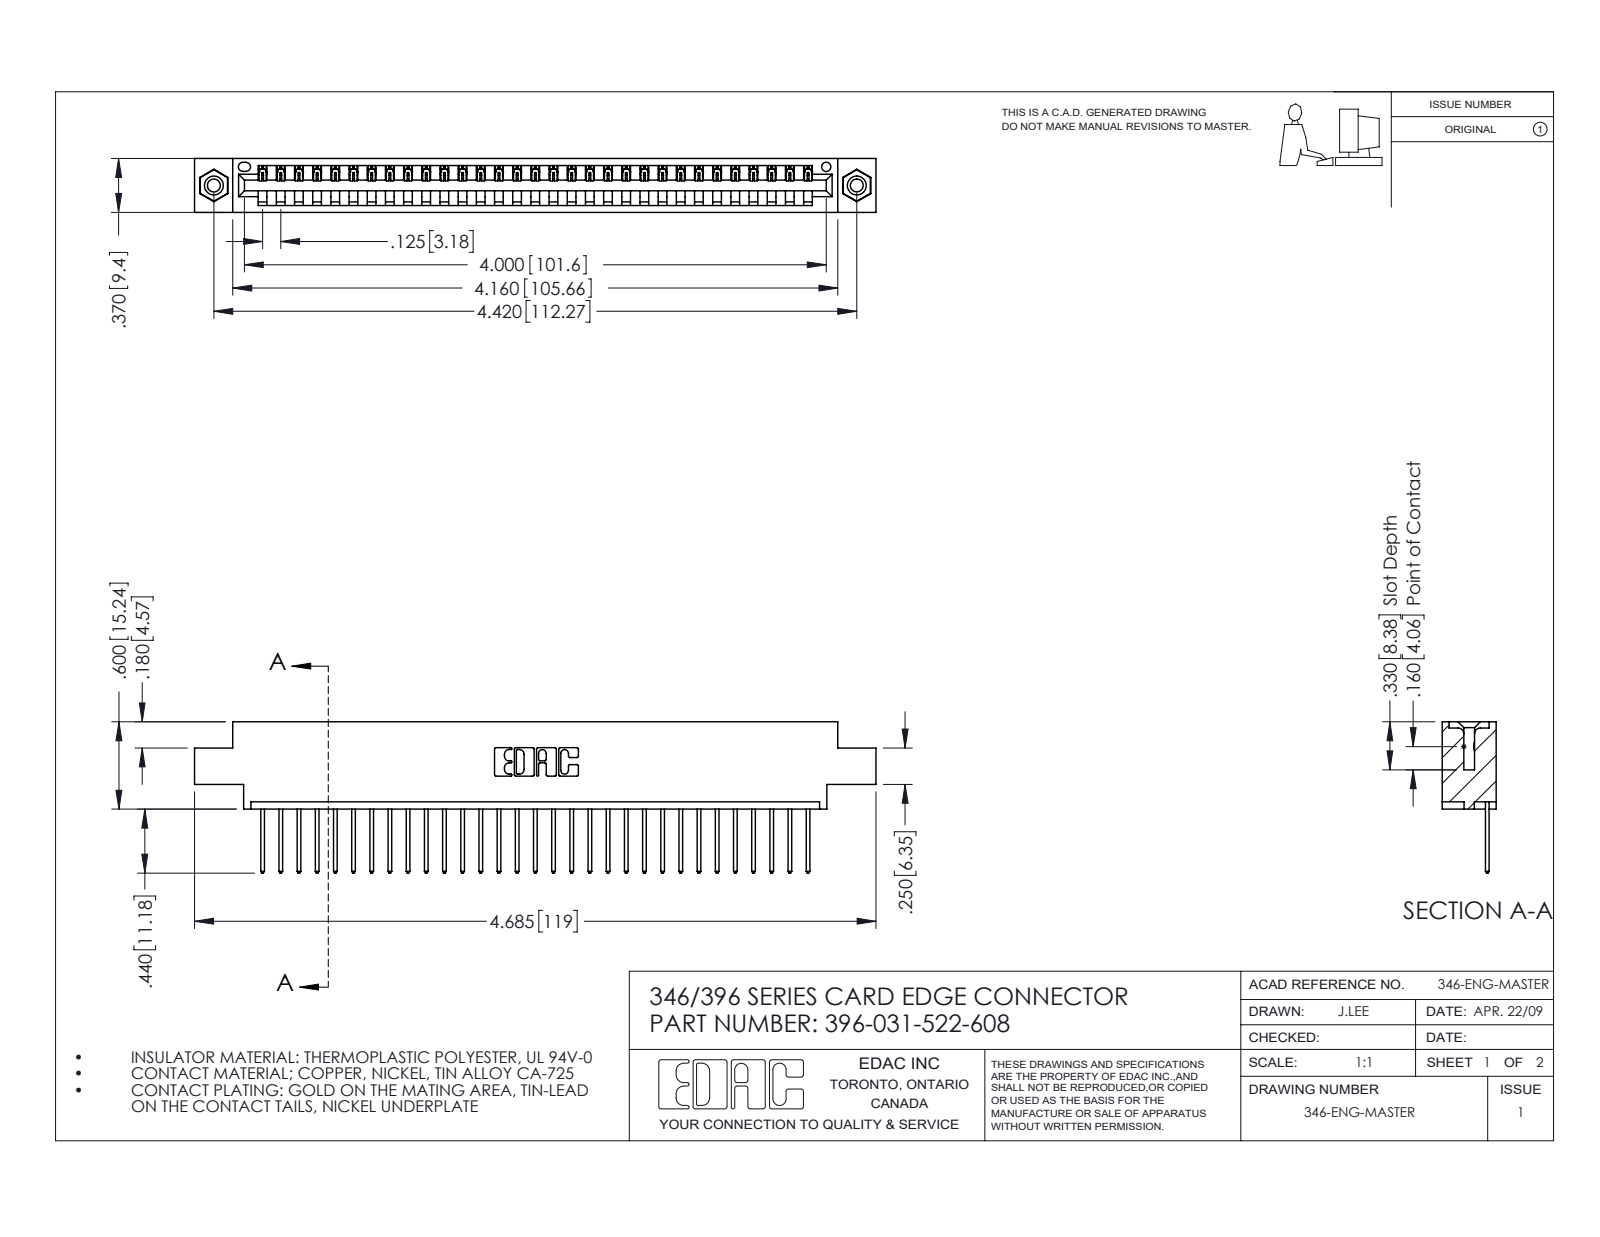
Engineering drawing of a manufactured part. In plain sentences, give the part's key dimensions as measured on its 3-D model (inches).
The part is named "345-250-001_345-250-003-102; 345-292-001_345-293-122; 346 Part_0.170 Offset - 0.156 Dia-TI; 396-031-522-608". Its 3-D file was written by "SolidWorks 2016 (CONFIG_CONTROL_DESIGN)". It is 34 solids with 1984 faces: 1352 planar, 616 cylindrical and 16 other. Overall it measures 4.685 by 1.04 by 0.37 inches. Its volume is 0.681 cubic inches and its surface area 21.89 square inches. Round holes: 2 of diameter 0.089, 2 of diameter 0.125, 2 of diameter 0.156, 1 of diameter 0.064. Round bosses or shafts: 2 of diameter 0.155. Partial cylindrical surfaces (rounded edges, fillets, slot ends): 62 of radius 0.006, 62 of radius 0.01, 22 of radius 0.01, 6 of radius 0.007, 6 of radius 0.031, 3 of radius 0.026, 2 of radius 0.031, 2 of radius 0.04. The main face-to-face distances are 0.048, 0.322, 0.37, 0.25, 0.072, 0.298, 0.025, 0.222, 0.148, 0.1. The hole center spacings are 0.246, 4.212, 4.42.
